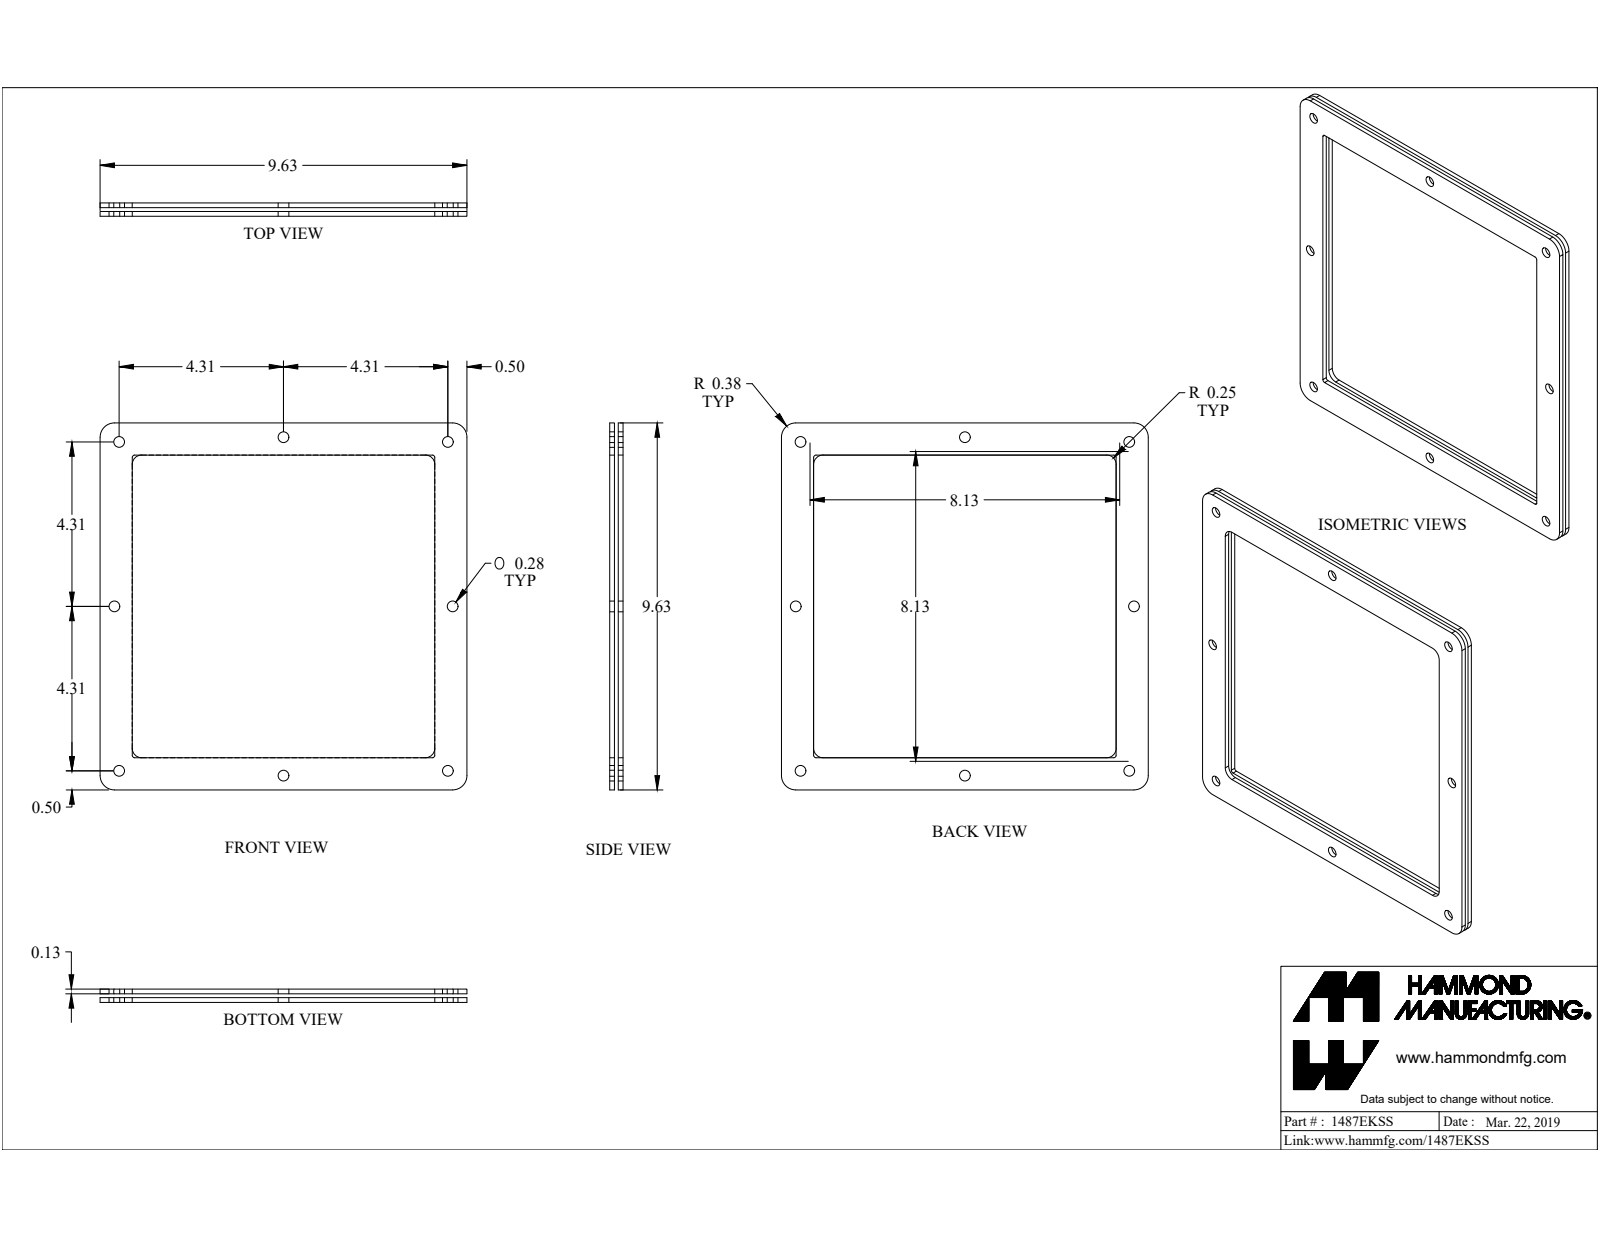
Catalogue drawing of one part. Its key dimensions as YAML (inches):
part_name: "1487EKSS"
step_written_by: "SolidWorks 2019 (CONFIG_CONTROL_DESIGN)"
units: inches
bodies: {solids: 7, faces: 217, planar: 126, cylindrical: 75, other: 16}
overall_size: [9.625, 9.625, 1.916]
volume: 7.43
surface_area: 139.4
round_holes:
  - {diameter: 0.281, count: 8}
  - {diameter: 0.258, count: 2}
  - {diameter: 0.35, count: 2}
  - {diameter: 0.196, count: 1}
round_bosses_or_shafts:
  - {diameter: 0.5, count: 2}
  - {diameter: 0.25, count: 2}
partial_cylinders:
  - {radius: 0.02, count: 12}
  - {radius: 0.25, count: 5}
  - {radius: 0.063, count: 4}
  - {radius: 0.375, count: 4}
face_to_face_distances: [0.125, 0.1, 0.225, 0.225, 0.35, 0.125, 9.625, 0.844, 8.781, 0.843]
hole_center_spacings: [4.315, 9.755, 4.437, 6.099, 6.276, 8.625, 8.875, 12.198]
